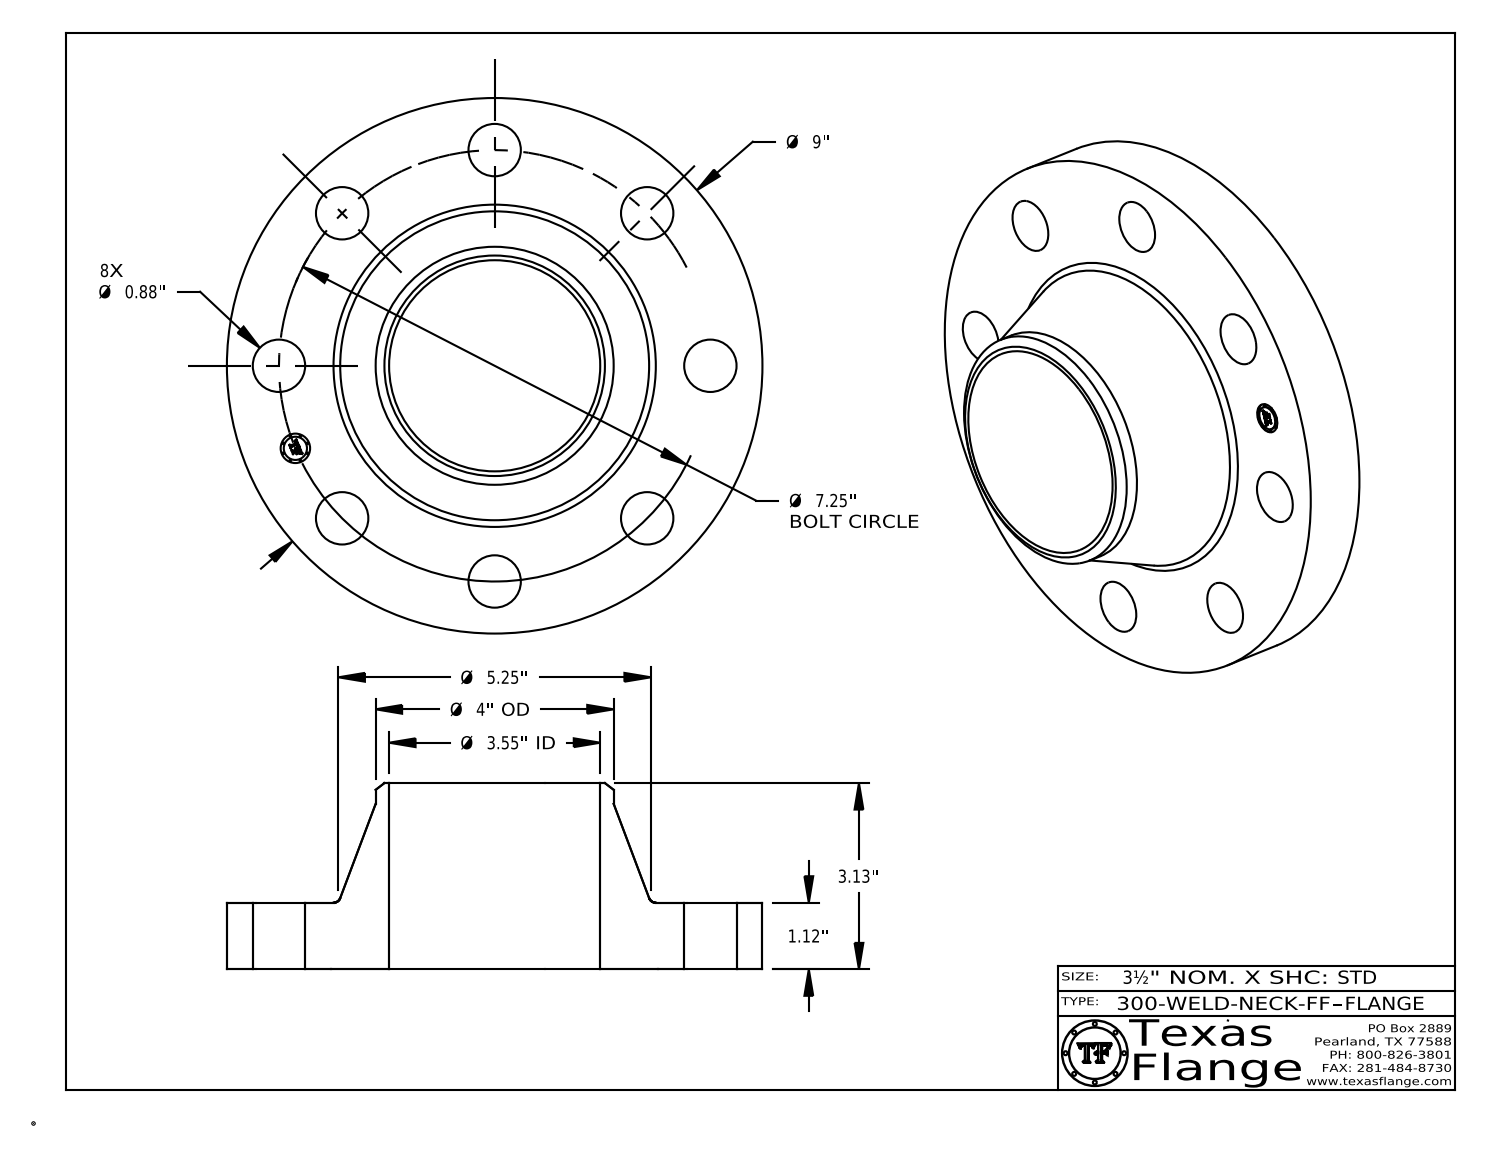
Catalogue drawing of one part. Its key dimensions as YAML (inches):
part_name: "300-WELD-NECK-FF"
step_written_by: "CATIA V5 STEP AP214 (AUTOMOTIVE_DESIGN)"
units: inches
bodies: {solids: 1, faces: 417, planar: 369, cylindrical: 42, other: 6}
overall_size: [9, 9, 3.13]
volume: 67.23
surface_area: 208.9
round_holes:
  - {diameter: 0.88, count: 8}
  - {diameter: 0.495, count: 1}
  - {diameter: 3.548, count: 1}
round_bosses_or_shafts:
  - {diameter: 0.03, count: 8}
  - {diameter: 9, count: 1}
  - {diameter: 4, count: 1}
  - {diameter: 0.39, count: 1}
face_to_face_distances: [1.12, 3.13, 2.01, 1.105, 0.015, 2.025, 0.148, 0.144, 0.027, 0.096]
hole_center_spacings: [3.625, 2.774, 5.127, 6.698, 7.25, 1.415, 7.111, 4.028]
